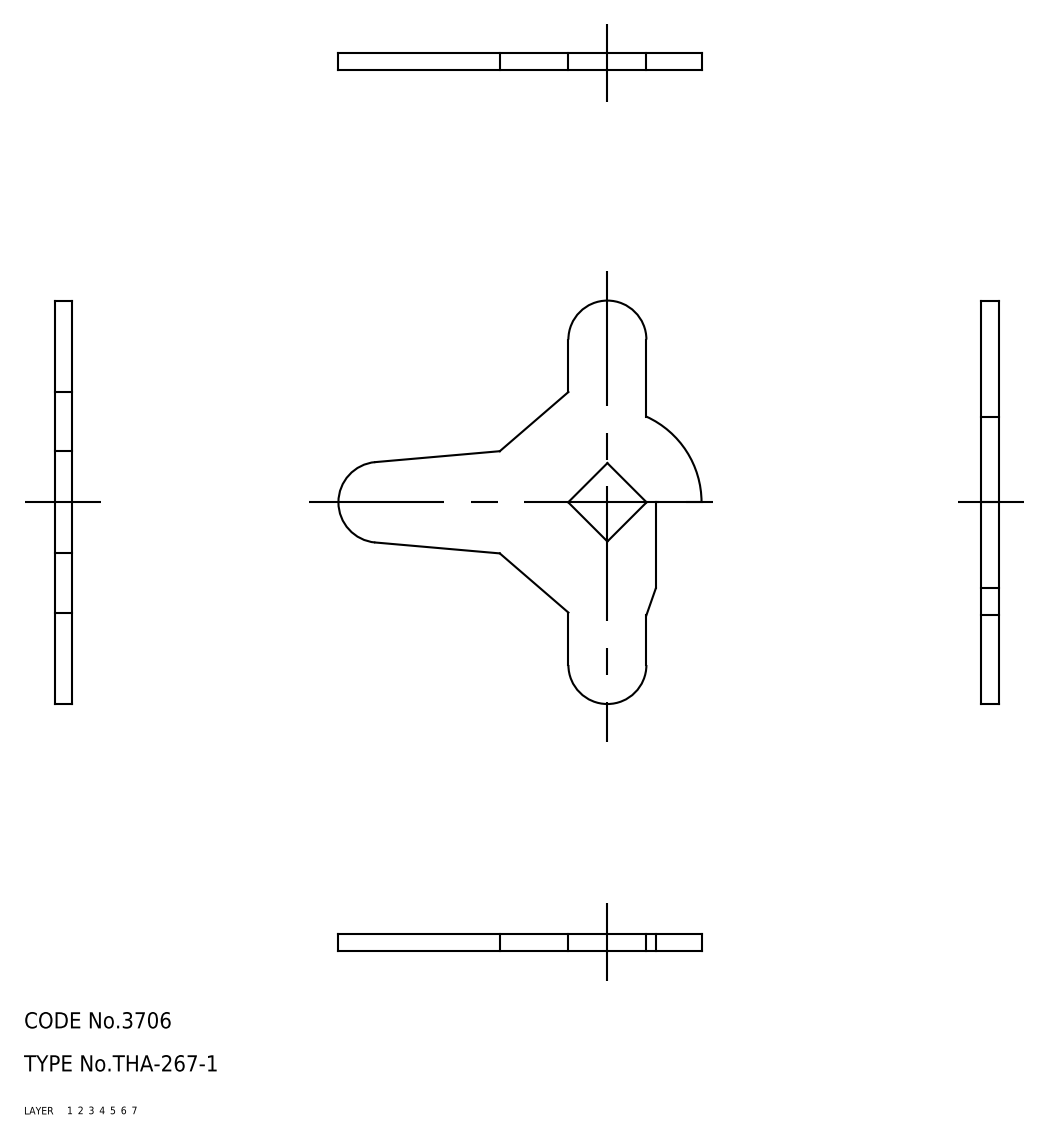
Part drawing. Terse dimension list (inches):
name: cam
written by: CADfix (AUTOMOTIVE_DESIGN)
unit: in
bodies: 1 solid, 21 faces (0 planar, 0 cylindrical, 21 other)
size: 2.953 × 2.657 × 0.126
volume: 0.379 in³; area: 7.414 in²
